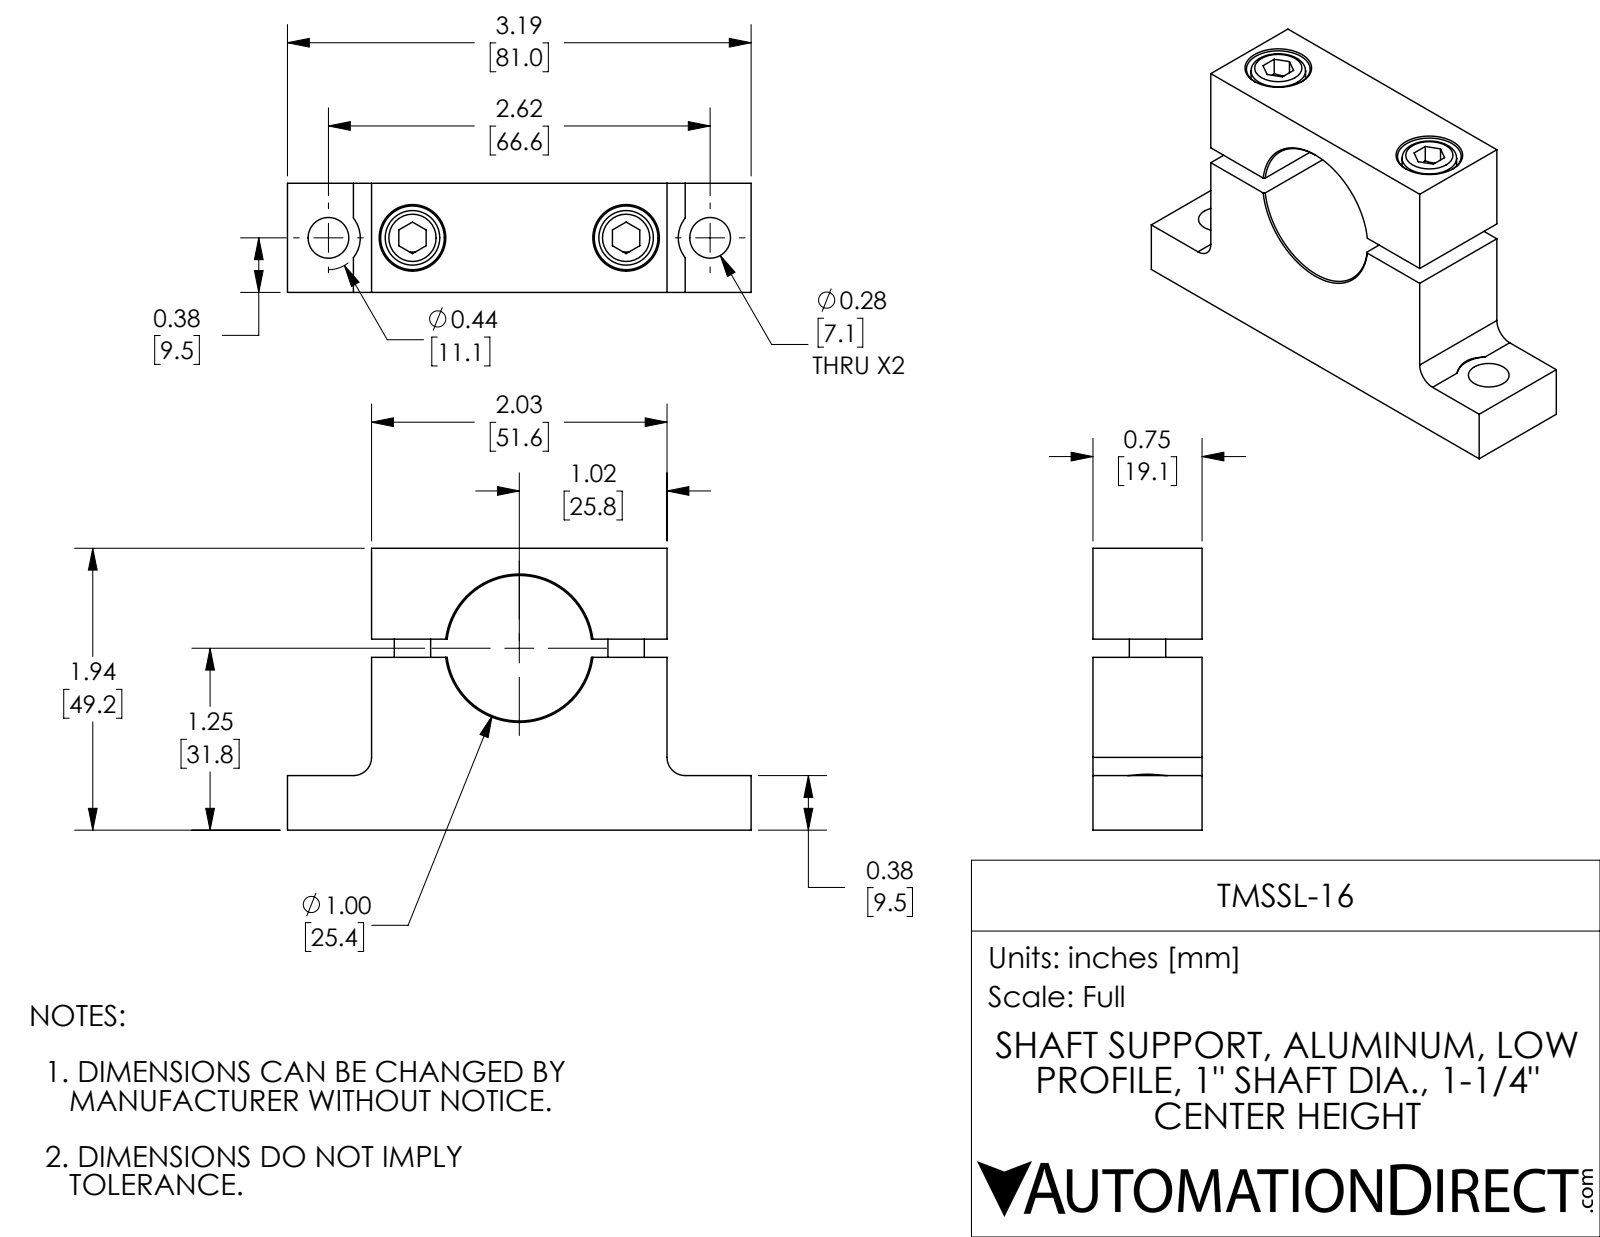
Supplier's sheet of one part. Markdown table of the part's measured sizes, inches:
| quantity | value |
| --- | --- |
| part name | TMSSL-16 |
| STEP written by | SolidWorks 2017 (AUTOMOTIVE_DESIGN) |
| units | inches |
| bodies | 4 solids, 93 faces (38 planar, 31 cylindrical, 24 other) |
| overall size | 3.188 × 1.937 × 0.75 |
| volume | 2.503 in³ |
| surface area | 23.58 in² |
| round holes (diameter × count) | 0.196 × 2, 0.266 × 2, 0.28 × 2, 0.438 × 2, 1 × 1 |
| round bosses / shafts (diameter × count) | 0.375 × 2, 0.25 × 2 |
| partial cylindrical surfaces (radius × count) | 0.125 × 2, 0.219 × 2 |
| main face-to-face distances | 0.75, 1.937, 2.031, 1.187, 0.75, 1.313, 0.125, 0.624, 0.375, 0.813 |
| hole center spacings | 0.578, 2.046, 1.469, 2.624 |
